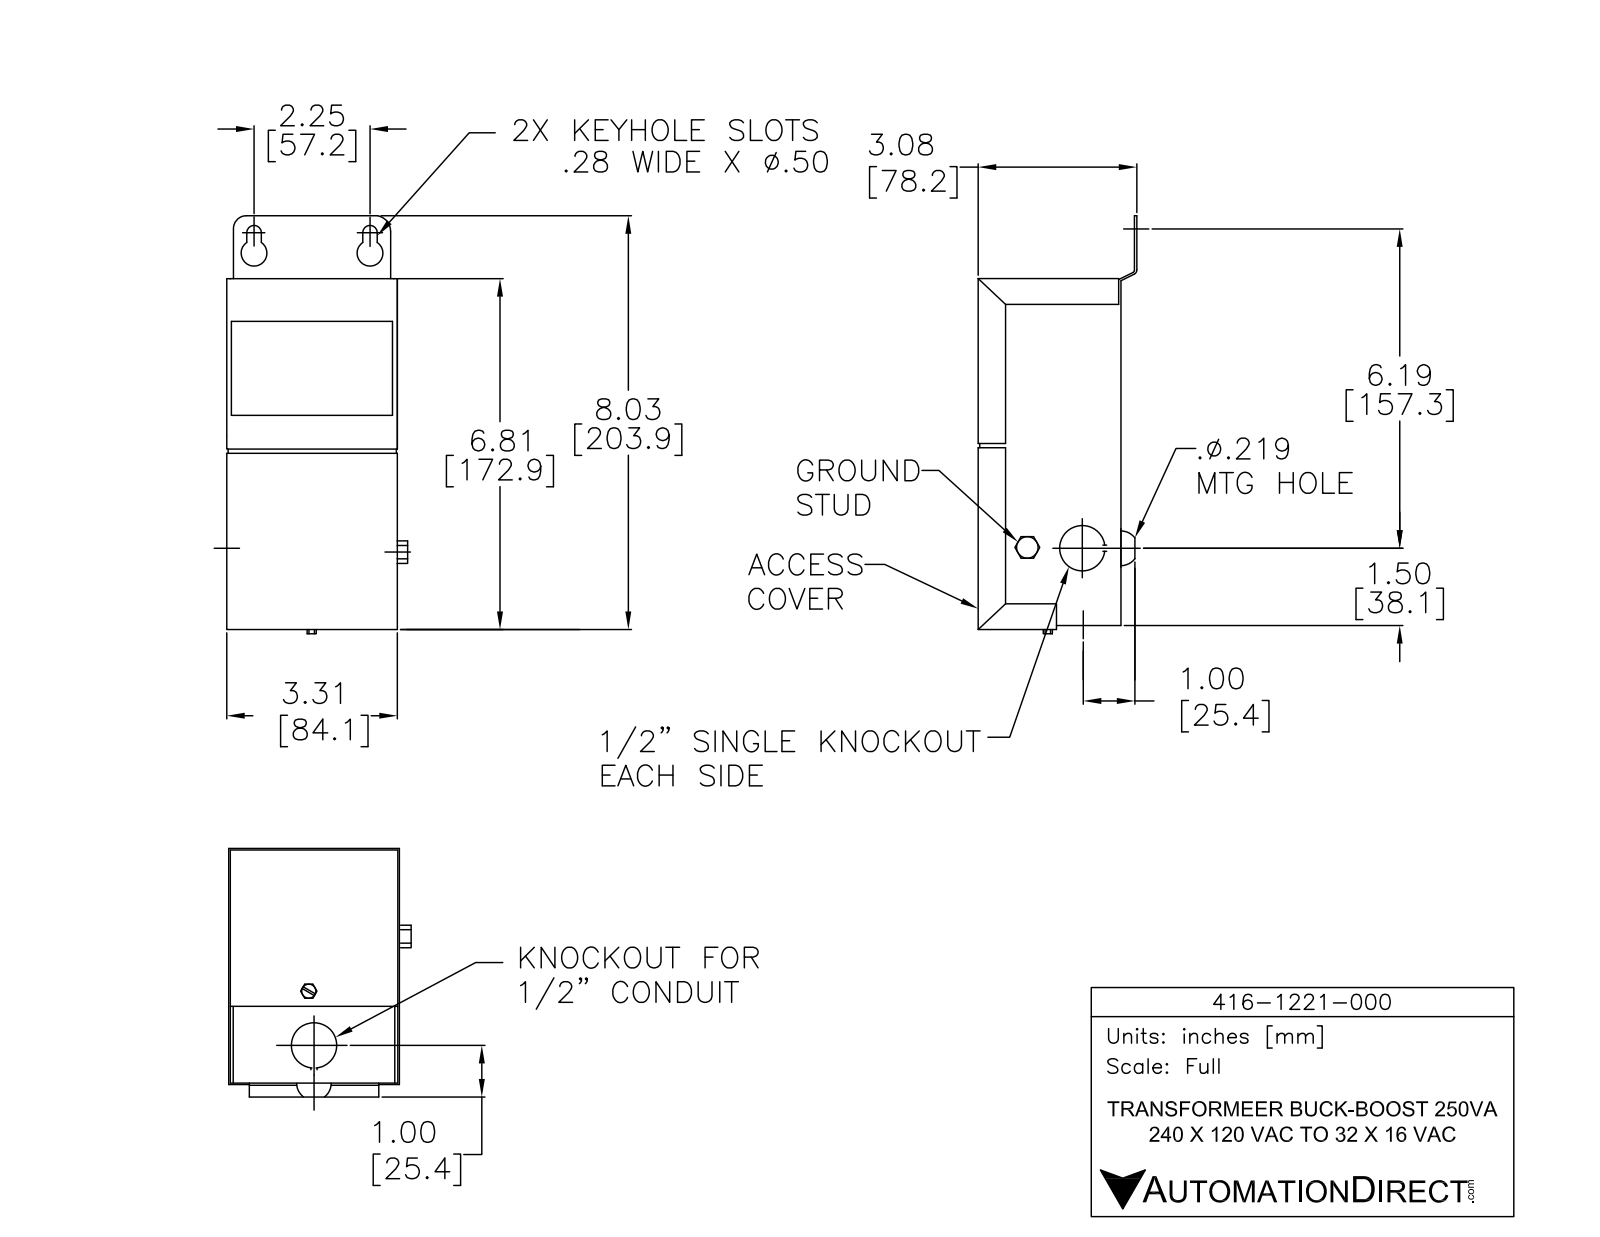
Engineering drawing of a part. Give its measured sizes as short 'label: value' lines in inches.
name: 416-1221-000
written by: SolidWorks 2013 (AUTOMOTIVE_DESIGN)
unit: in
bodies: 1 solid, 150 faces (89 planar, 45 cylindrical, 16 other)
size: 8.14 × 3.42 × 3.081
volume: 63.4 in³; area: 112.7 in²
holes: 2× ⌀0.5, 2× ⌀0.875, 1× ⌀0.185, 1× ⌀0.231, 1× ⌀0.275
rounds: 10× R0.04, 10× R0.25, 2× R0.14, 1× R0.06, 1× R0.1
face distances: 2.861, 3.23, 0.04, 3.27, 0.04, 2.86, 3.31, 6.81, 6.77, 0.22
hole spacings: 5.908, 0.763, 0.862, 2.25
